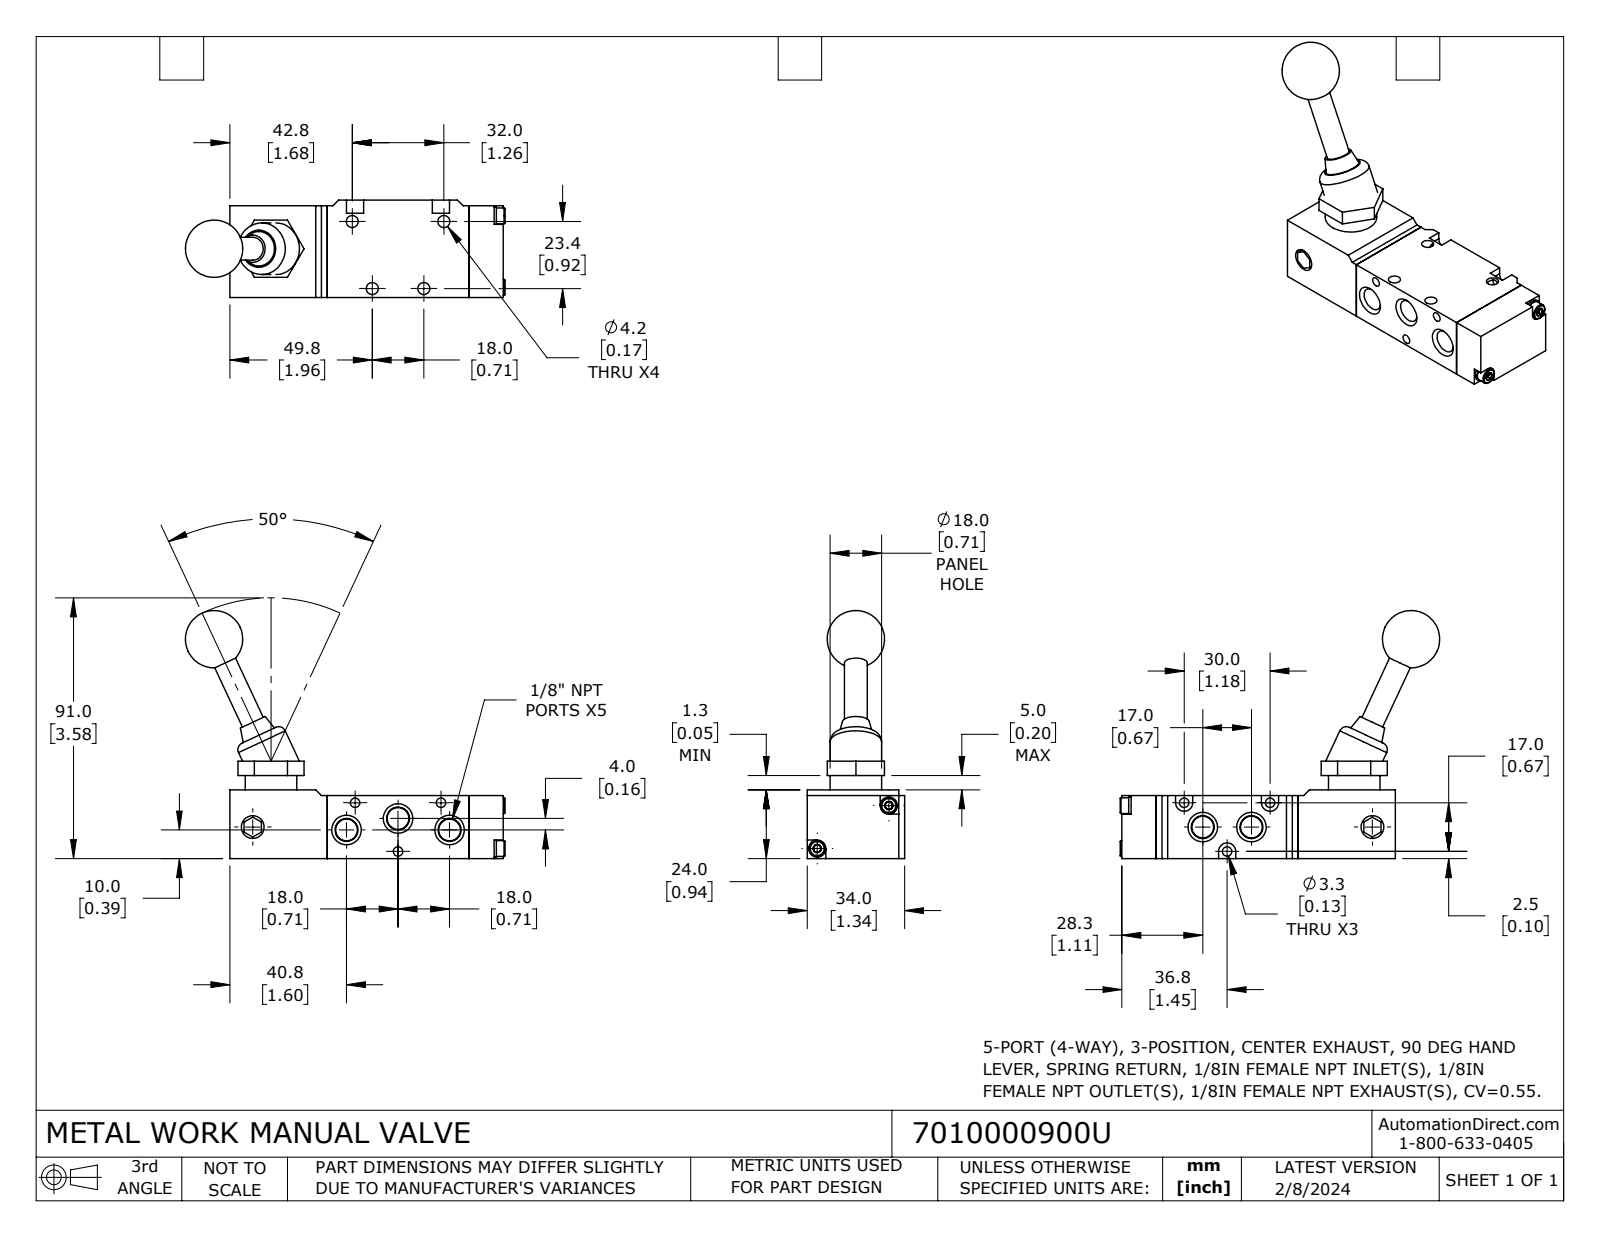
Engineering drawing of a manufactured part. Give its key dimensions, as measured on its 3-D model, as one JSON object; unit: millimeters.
{"part_name": "7010000900U", "step_written_by": "SolidWorks 2023 (CONFIG_CONTROL_DESIGN)", "units": "millimeters", "bodies": {"solids": 8, "faces": 208, "planar": 105, "cylindrical": 49, "other": 54}, "overall_size": [111.6, 86.6, 34], "volume_mm3": 79120, "surface_area_mm2": 22500, "round_holes": [[4.2, 4], [3.3, 3], [3, 2], [8, 1]], "round_bosses_or_shafts": [[18, 2], [6, 2], [5.5, 2], [8, 1]], "partial_cylinders_radius": [[3, 3]], "face_to_face_distances": [22, 34, 49.5, 2, 32, 12, 83.5, 24, 61.5, 95.5], "hole_center_spacings": [22.7, 24.4, 34.2, 18, 29.2, 30, 32, 36.8]}
